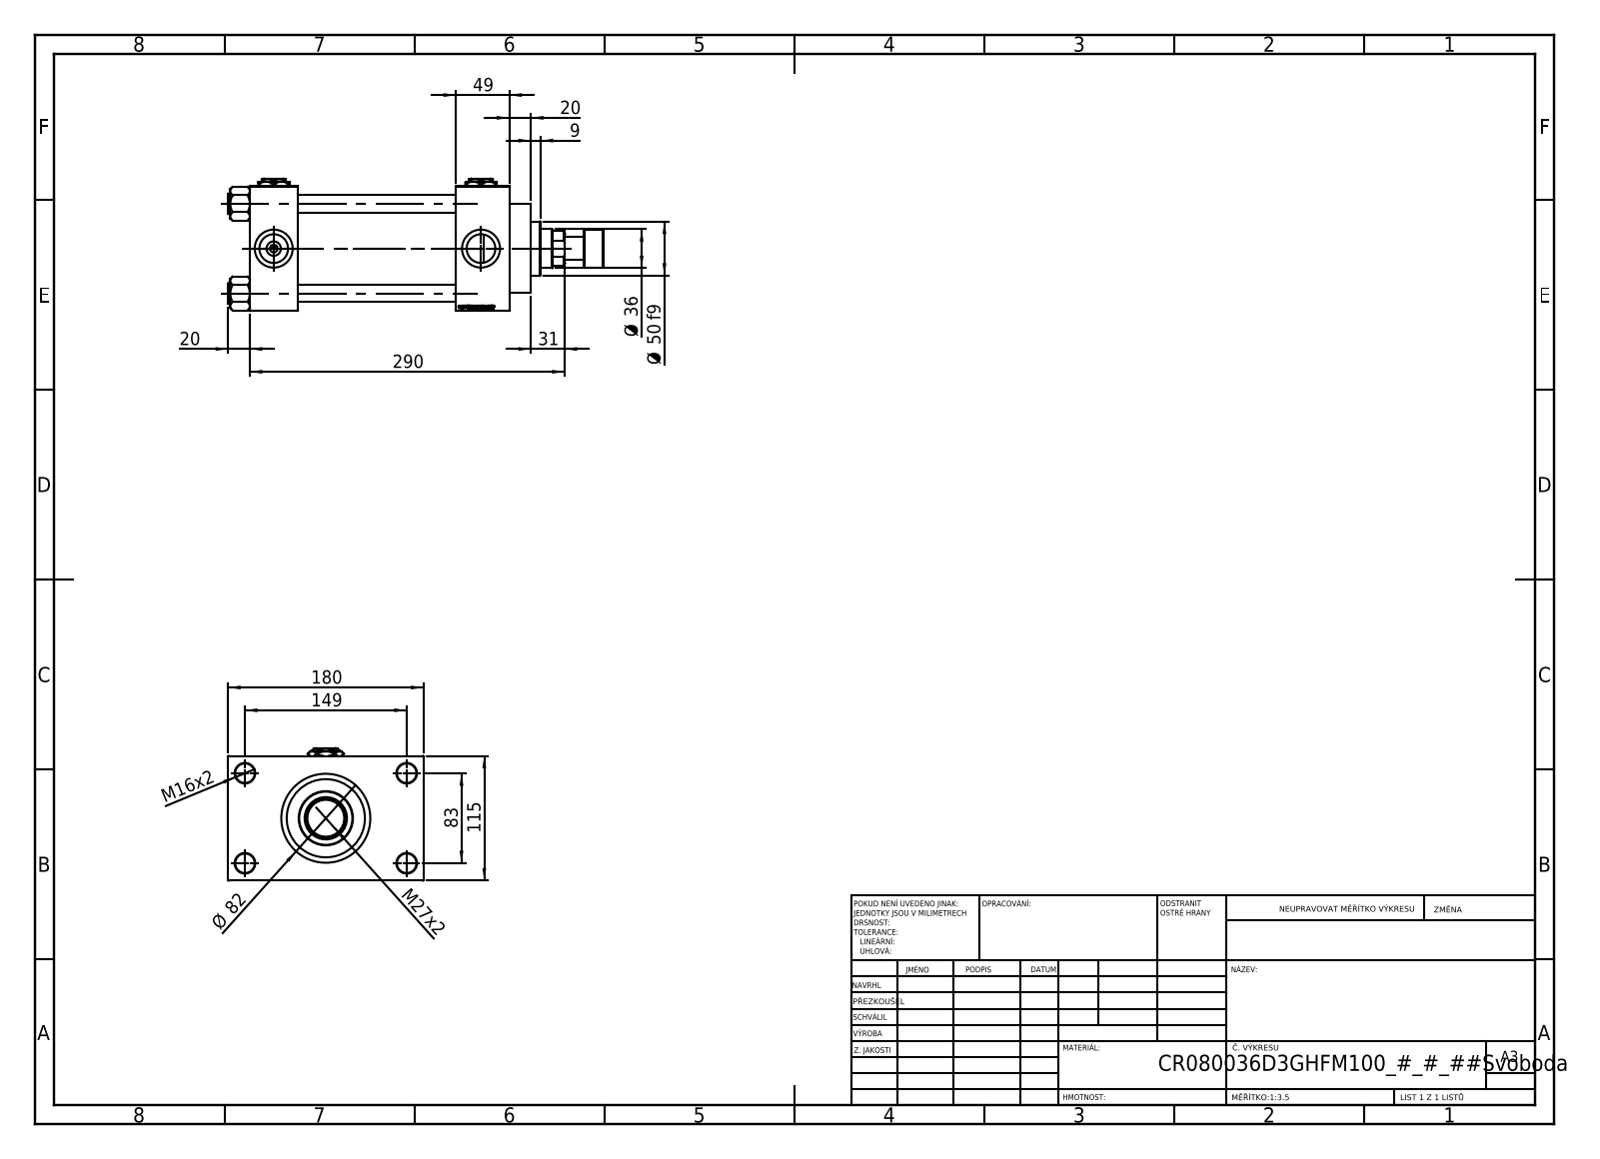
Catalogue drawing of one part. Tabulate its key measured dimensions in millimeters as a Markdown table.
| quantity | value |
| --- | --- |
| part name | Zatka_pro_OIL_PORT; V215CR_ROD_END_F; V215CR_D_Body; V215_VC_A (+3 more) |
| STEP written by | SolidWorks 2019 (CONFIG_CONTROL_DESIGN) |
| units | millimeters |
| bodies | 14 solids, 1266 faces (597 planar, 103 cylindrical, 566 other) |
| overall size | 346 × 180 × 122 |
| volume | 2 198 000 mm³ |
| surface area | 375 725 mm² |
| round holes (diameter × count) | 16 × 4, 18 × 4, 26.44 × 4, 35 × 4, 7 × 3, 25.5 × 1, 36 × 1, 39 × 1, 61 × 1, 72 × 1, 80 × 1 |
| round bosses / shafts (diameter × count) | 19 × 4, 86 × 1, 82 × 1, 50 × 1, 35 × 1, 21 × 1 |
| main face-to-face distances | 115, 146, 49, 195, 44, 190, 239, 32.5, 147.5, 100 |
| hole center spacings | 33.15, 58.48, 82.7, 85.28, 89.24, 115.85, 142.43, 83 |
